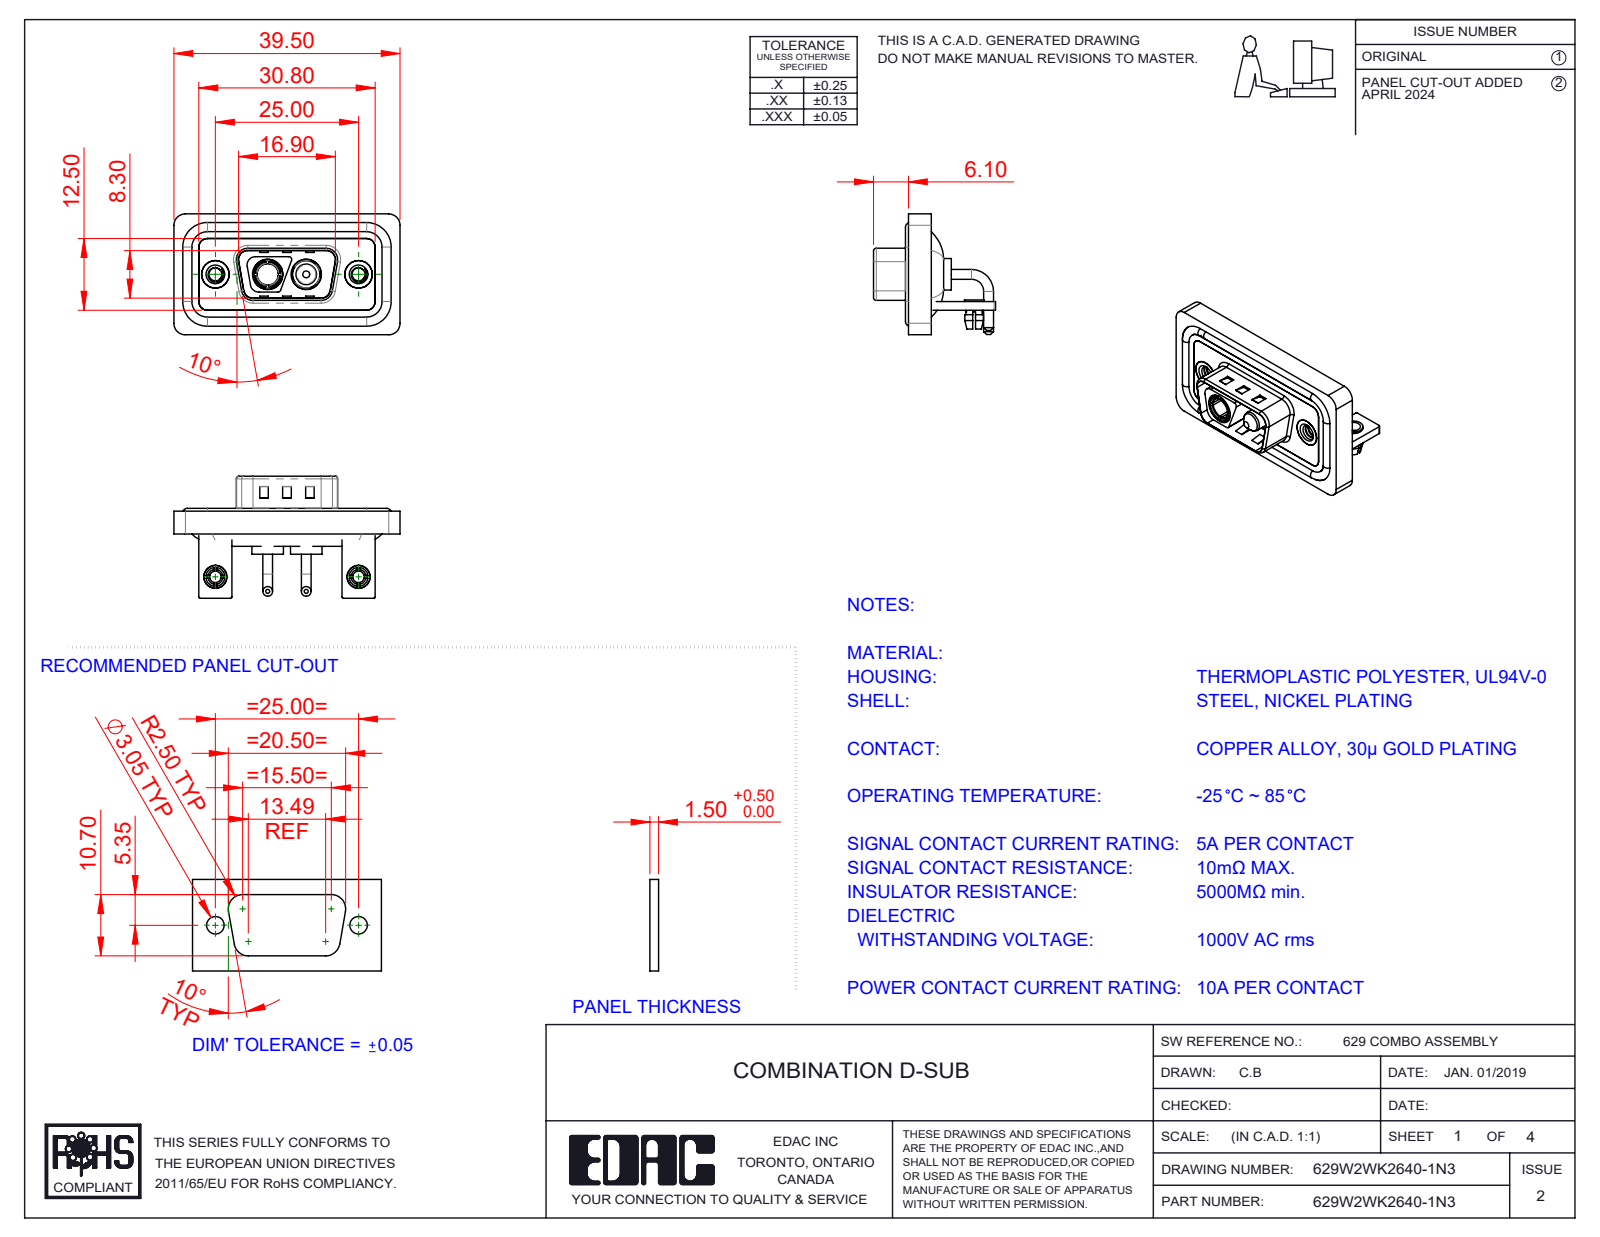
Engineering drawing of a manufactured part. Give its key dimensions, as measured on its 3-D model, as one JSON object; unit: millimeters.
{"part_name": "629Combo Threaded Rivet_3; 629Combo Housing_2WK2; 629Combo Board Lock; 629Combo Shell Front_09 Contacts (+6 more)", "step_written_by": "SolidWorks 2023 (CONFIG_CONTROL_DESIGN)", "units": "millimeters", "bodies": {"solids": 15, "faces": 674, "planar": 257, "cylindrical": 281, "other": 136}, "overall_size": [39.5, 21.3, 21.1], "volume_mm3": 4877, "surface_area_mm2": 8225, "round_holes": [[2, 2], [2.26, 2], [2.5, 2], [3.2, 2], [4, 2], [4.8, 2], [4.85, 2], [5, 2], [5.3, 2], [3.7, 1]], "round_bosses_or_shafts": [[1.7, 4], [1.6, 4], [5.5, 2], [5.2, 2], [4.9, 2], [4.75, 2], [4, 2], [3.75, 2]], "partial_cylinders_radius": [[1.5, 20], [2, 19], [0.25, 16], [0.5, 11], [1.6, 8], [0.6, 4], [0.65, 4], [0.9, 4]], "face_to_face_distances": [0.4, 1.5, 2.9, 0.8, 1.1, 1.2, 2.1, 1.6, 3.7, 2.5], "hole_center_spacings": [9.14, 15.86, 25, 6.72]}
